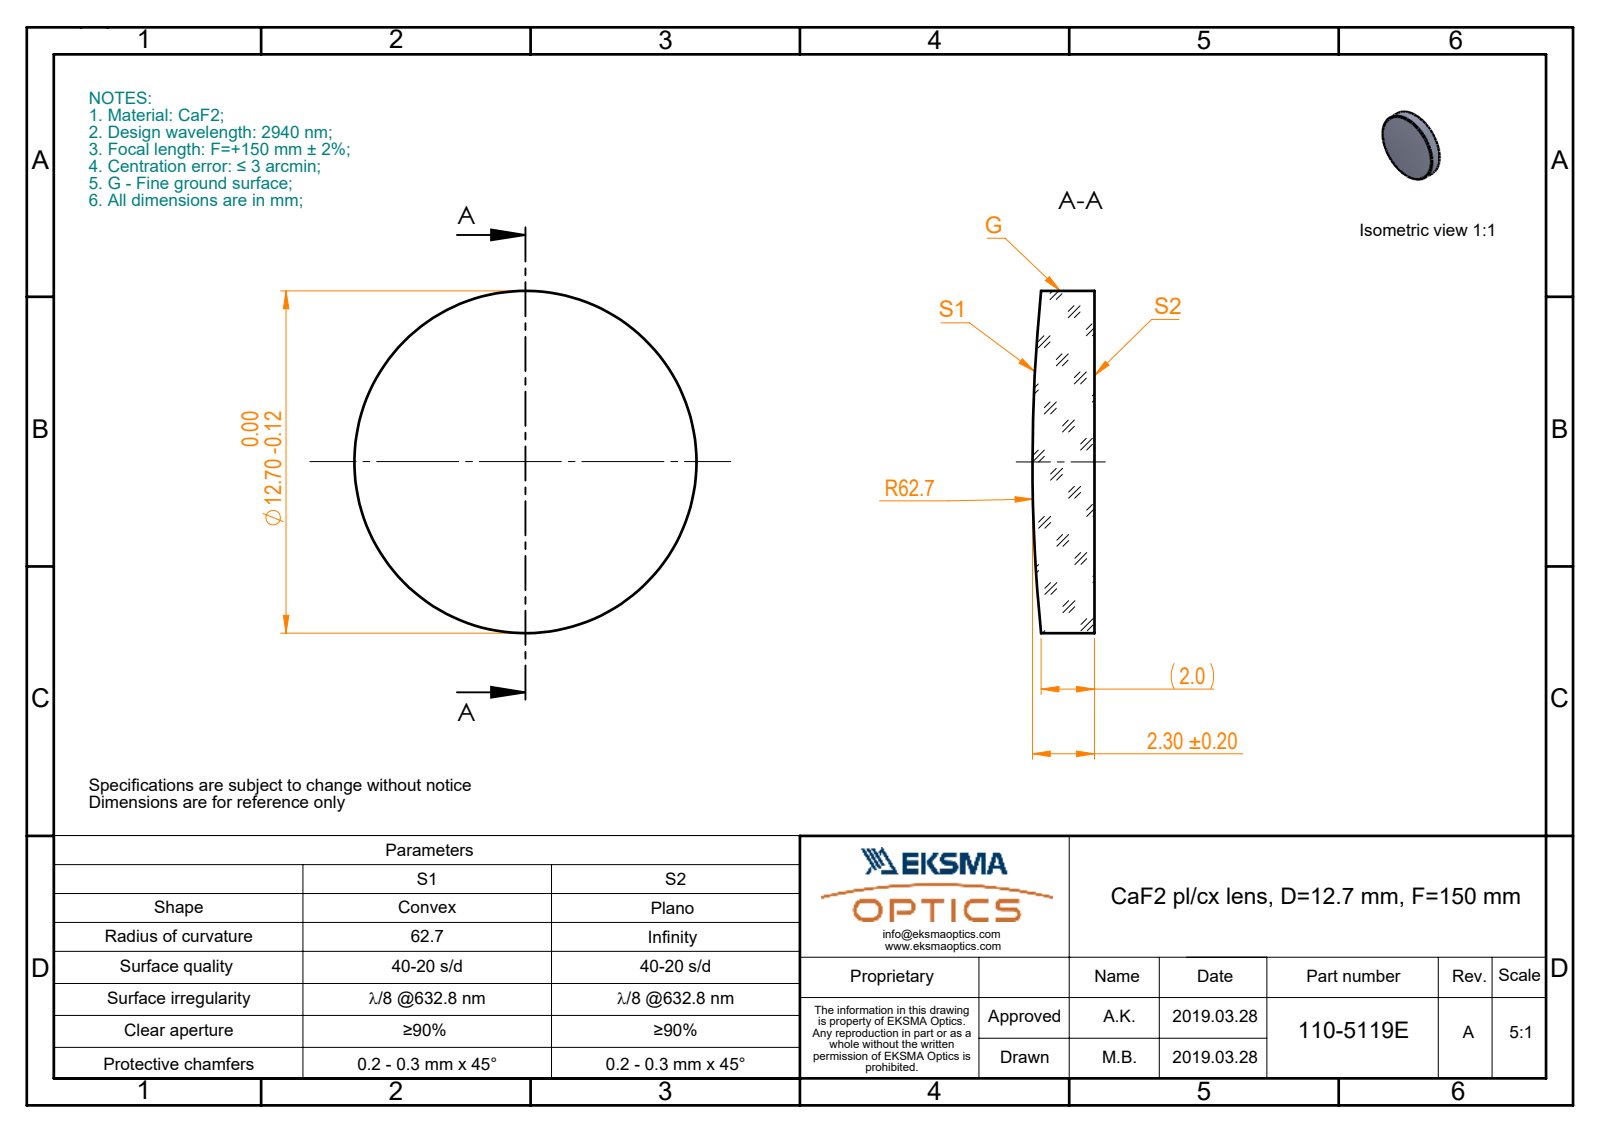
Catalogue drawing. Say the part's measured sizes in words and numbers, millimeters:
The part is named "110-5119E CaF2 pl-cx 12.7 F150". Its 3-D file was written by "SolidWorks 2017 (CONFIG_CONTROL_DESIGN)". It is 1 solid with 5 faces: 1 planar, 2 cylindrical and 2 other. Overall it measures 12.7 by 12.7 by 2.3 millimeters. Its volume is 271 cubic millimeters and its surface area 333 square millimeters. Round bosses or shafts: 1 of diameter 12.7.
